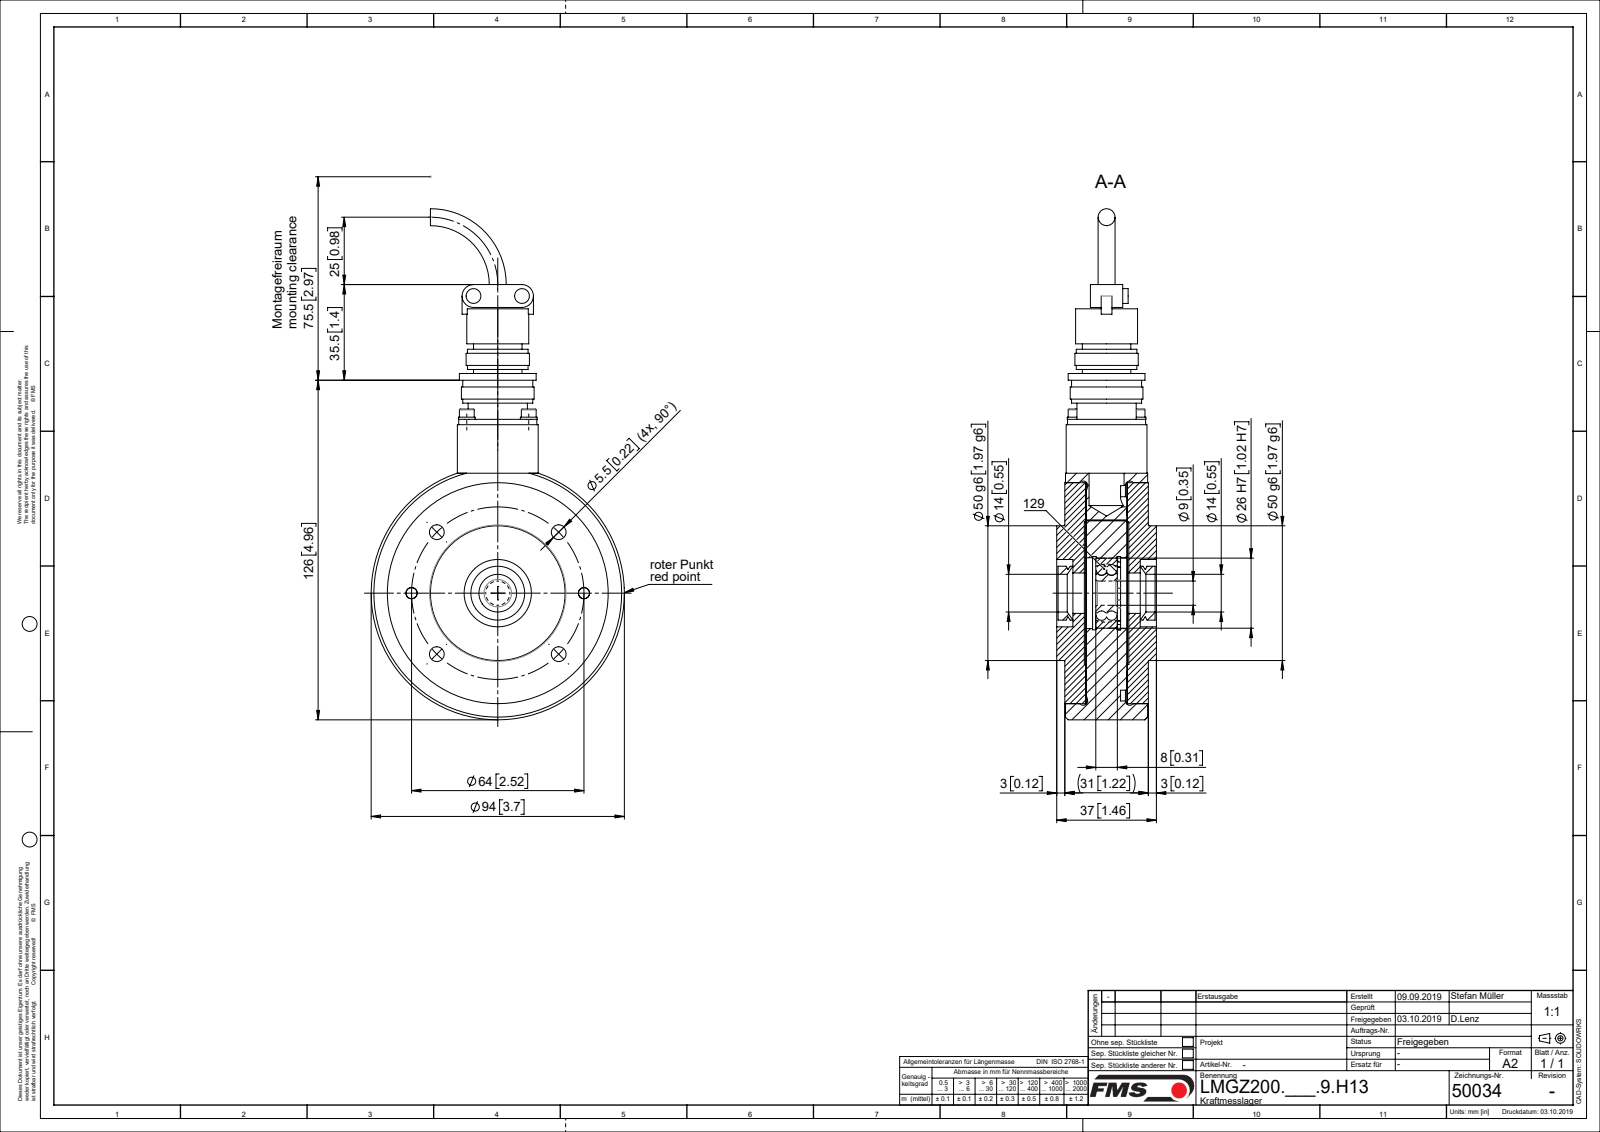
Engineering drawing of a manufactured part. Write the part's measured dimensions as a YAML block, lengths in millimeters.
part_name: "L50034; L4900504; L49014; TEIL1 (+8 more)"
step_written_by: "Mechanical Desktop 2007 (CONFIG_CONTROL_DESIGN)"
units: millimeters
bodies: {solids: 21, faces: 413, planar: 125, cylindrical: 237, other: 51}
overall_size: [169.5, 117, 37]
volume: 251032
surface_area: 90846
round_holes:
  - {diameter: 5.5, count: 6}
  - {diameter: 2.6, count: 4}
  - {diameter: 3.2, count: 4}
  - {diameter: 3.4, count: 4}
  - {diameter: 3.5, count: 4}
  - {diameter: 4.33, count: 4}
  - {diameter: 6.6, count: 4}
  - {diameter: 10, count: 2}
  - {diameter: 9, count: 1}
  - {diameter: 14, count: 1}
  - {diameter: 15, count: 1}
  - {diameter: 16.1, count: 1}
round_bosses_or_shafts:
  - {diameter: 6.2, count: 4}
  - {diameter: 5.5, count: 4}
  - {diameter: 3, count: 4}
  - {diameter: 8, count: 3}
  - {diameter: 22, count: 2}
  - {diameter: 6.5, count: 2}
  - {diameter: 5, count: 2}
  - {diameter: 4.8, count: 2}
partial_cylinders:
  - {radius: 2.5, count: 2}
  - {radius: 8, count: 2}
  - {radius: 3.5, count: 1}
  - {radius: 5, count: 1}
face_to_face_distances: [15.25, 15, 23.25, 8, 7.75, 23, 15.5, 0.5, 7.25, 16]
hole_center_spacings: [32, 16.26, 23, 24.49, 45.26, 59.13, 62.77, 12.48]
